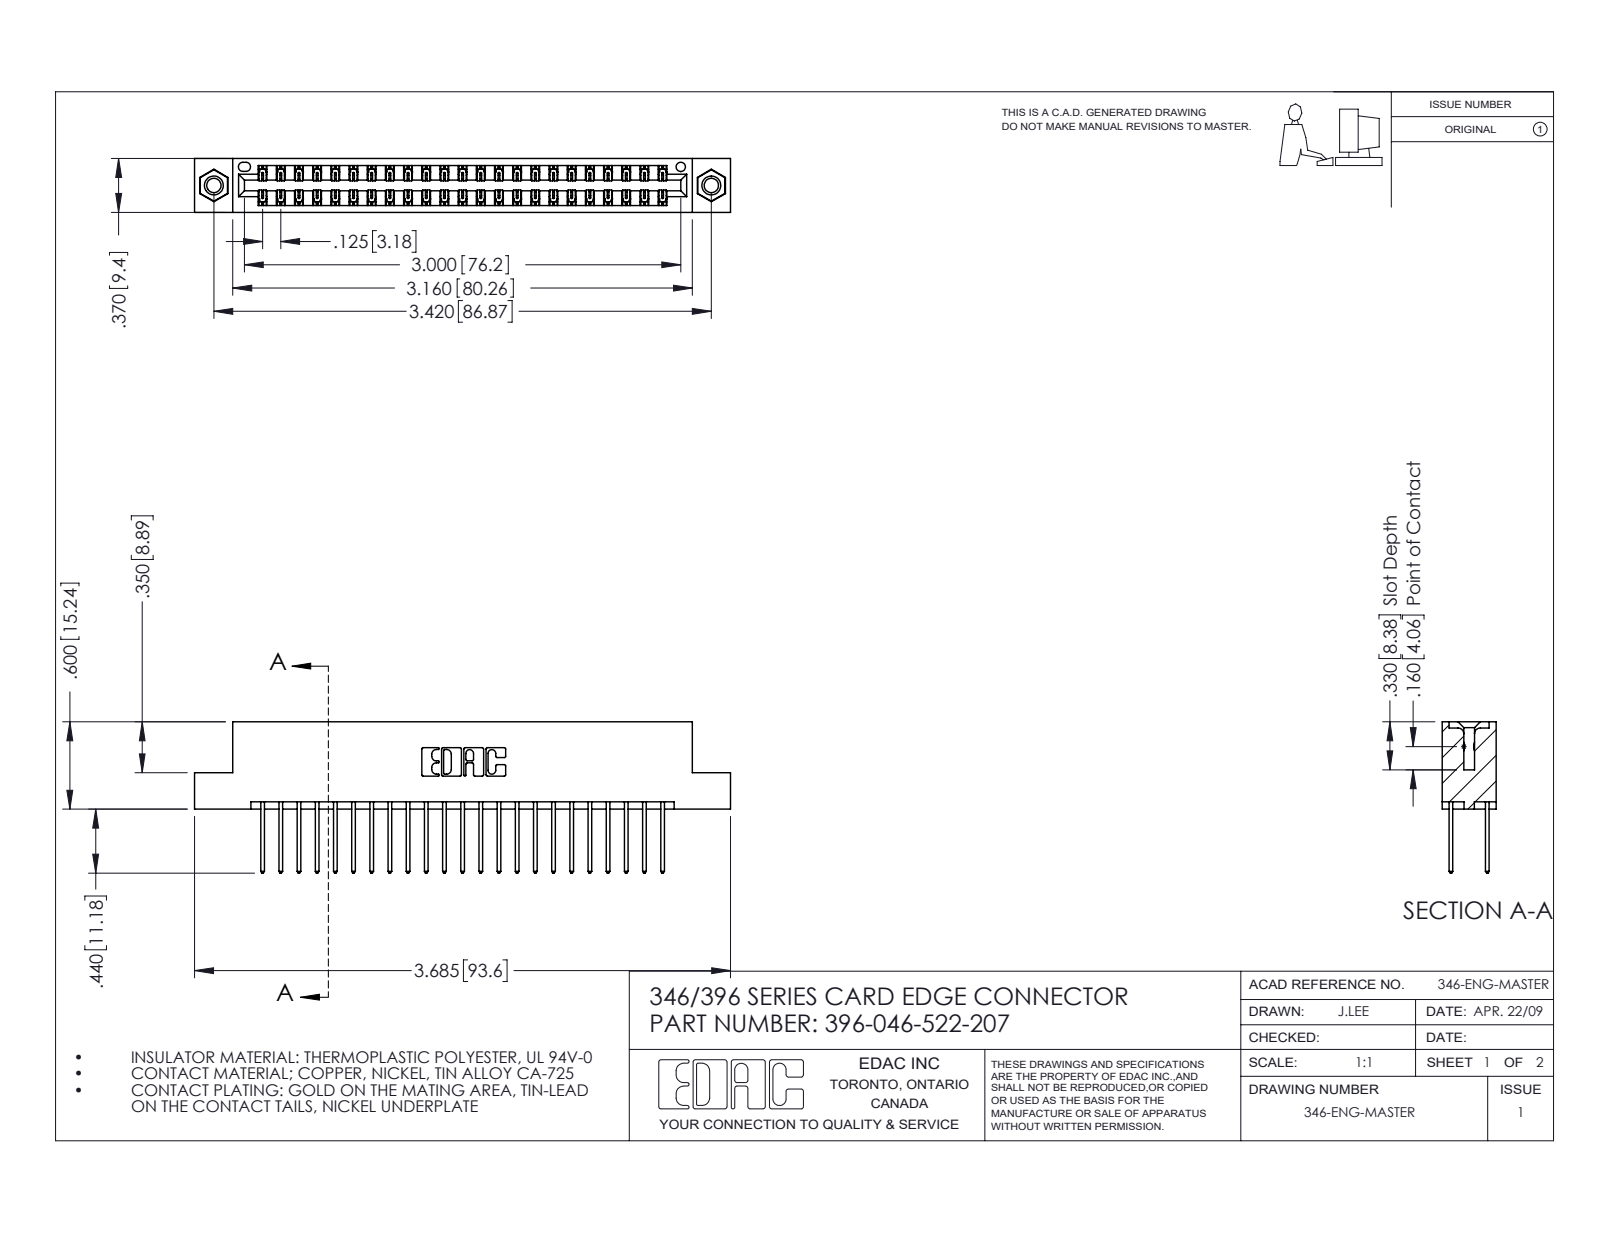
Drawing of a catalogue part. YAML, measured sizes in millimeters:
part_name: "396-046-522-207; 345-292-001_345-293-122; 345-250-001_345-250-005-103; 346 Part_Flush Mounting Lugs - 0.156 Dia-TI"
step_written_by: "SolidWorks 2016 (CONFIG_CONTROL_DESIGN)"
units: millimeters
bodies: {solids: 49, faces: 2574, planar: 1718, cylindrical: 840, other: 16}
overall_size: [93.6, 26.4, 9.4]
volume: 9080
surface_area: 12770
round_holes:
  - {diameter: 2.5, count: 2}
  - {diameter: 3.2, count: 2}
  - {diameter: 4, count: 2}
  - {diameter: 1.6, count: 1}
round_bosses_or_shafts:
  - {diameter: 3.9, count: 2}
partial_cylinders:
  - {radius: 0.2, count: 69}
  - {radius: 0.3, count: 46}
  - {radius: 0.3, count: 22}
  - {radius: 0.2, count: 6}
  - {radius: 0.8, count: 6}
  - {radius: 0.7, count: 3}
  - {radius: 0.4, count: 2}
  - {radius: 0.6, count: 2}
face_to_face_distances: [1.2, 8.2, 6.4, 9.4, 1.8, 7.6, 0.6, 7, 3.8, 5.6]
hole_center_spacings: [6.2, 81.6, 86.9]
